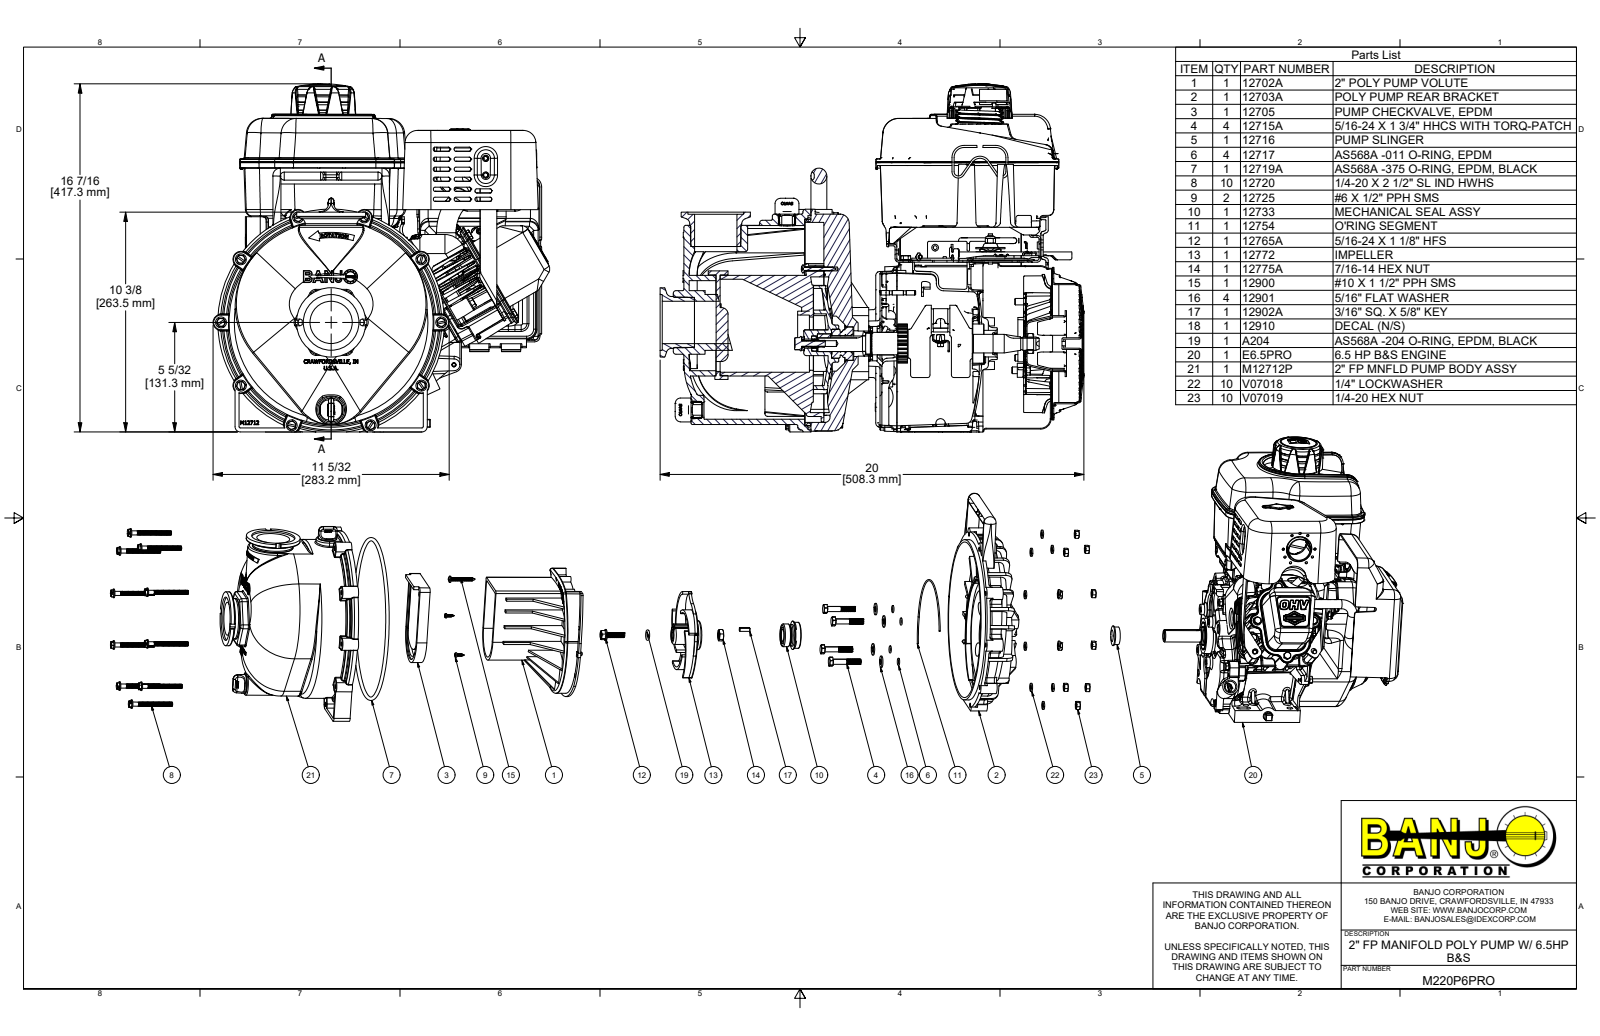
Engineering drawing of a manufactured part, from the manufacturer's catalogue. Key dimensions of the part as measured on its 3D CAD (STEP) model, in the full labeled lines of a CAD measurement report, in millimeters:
Part name (STEP PRODUCT): M220P6PRO; 12703A; 12716; M12712 (+8 more)
STEP written by: Autodesk Inventor 2019 (AUTOMOTIVE_DESIGN)
Units: millimetres
Bodies: 86 solids, 20084 faces (5422 planar, 5560 cylindrical, 9102 other)
Overall size (bounding box): 532.5 × 452.2 × 403.9
Volume: 2 935 000 mm³ · Surface area: 3 247 000 mm²
Round holes (diameter × count): ⌀6.4 ×13, ⌀6.9 ×11, ⌀5 ×10, ⌀6.4 ×10, ⌀3.5 ×9, ⌀3.6 ×7, ⌀5.6 ×7, ⌀8.1 ×6, ⌀6.9 ×5, ⌀7.1 ×5, ⌀5.5 ×4, ⌀7.5 ×4
Round bosses / shafts (diameter × count): ⌀7 ×80, ⌀6.4 ×14, ⌀12.7 ×12, ⌀13.2 ×10, ⌀12.4 ×10, ⌀4.8 ×8, ⌀7 ×6, ⌀4.9 ×6
Partial cylindrical surfaces — rounded edges, fillets, slot ends (radius × count): R0.8 ×372, R1.5 ×371, R3 ×201, R6.4 ×110, R2.3 ×109, R2 ×76, R1.5 ×72, R0.4 ×71
Main face-to-face distances: 0.9, 4.6, 1, 2, 0.7, 5.1, 2.2, 206.2, 1.2, 73.2
Hole centre spacings: 25, 132.1, 43.3, 12.9, 35.4, 79.5, 14.2, 17.9
